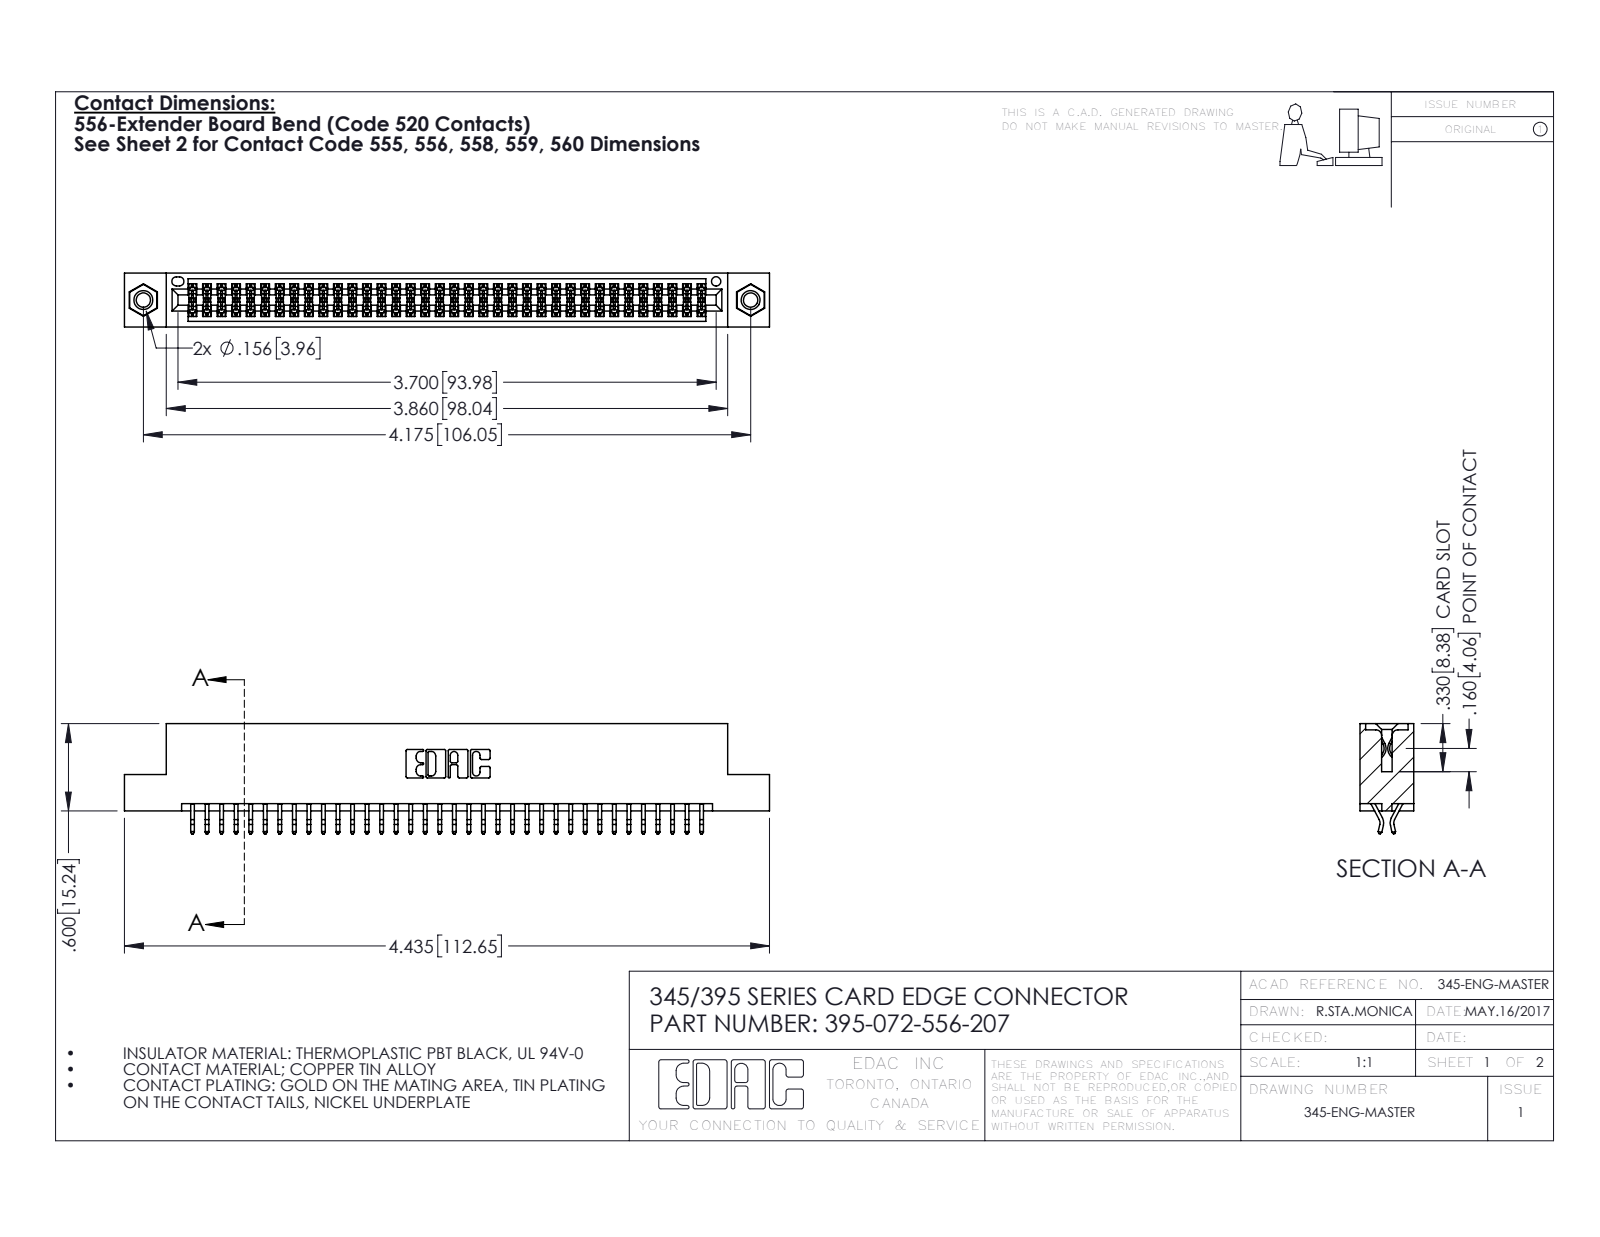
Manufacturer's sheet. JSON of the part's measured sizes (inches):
{"part_name": "345 Part_Flush Mounting Lugs - 0.156 Dia-TI; 395-072-556-207; 345-292-001_556 Tail; 345-250-001_345-250-005-103", "step_written_by": "SolidWorks 2016 (CONFIG_CONTROL_DESIGN)", "units": "inches", "bodies": {"solids": 75, "faces": 4218, "planar": 2776, "cylindrical": 1426, "other": 16}, "overall_size": [4.435, 0.757, 0.37], "volume_in3": 0.663, "surface_area_in2": 24.67, "round_holes": [[0.098, 2], [0.125, 2], [0.156, 2], [0.064, 1]], "round_bosses_or_shafts": [[0.155, 2]], "partial_cylinders_radius": [[0.006, 108], [0.01, 22], [0.007, 6], [0.031, 6], [0.026, 3], [0.01, 2], [0.014, 2], [0.019, 2]], "face_to_face_distances": [0.072, 0.298, 0.37, 0.2, 0.025, 0.098, 0.272, 0.225, 0.175, 0.149], "hole_center_spacings": [0.27, 3.939, 4.175]}
